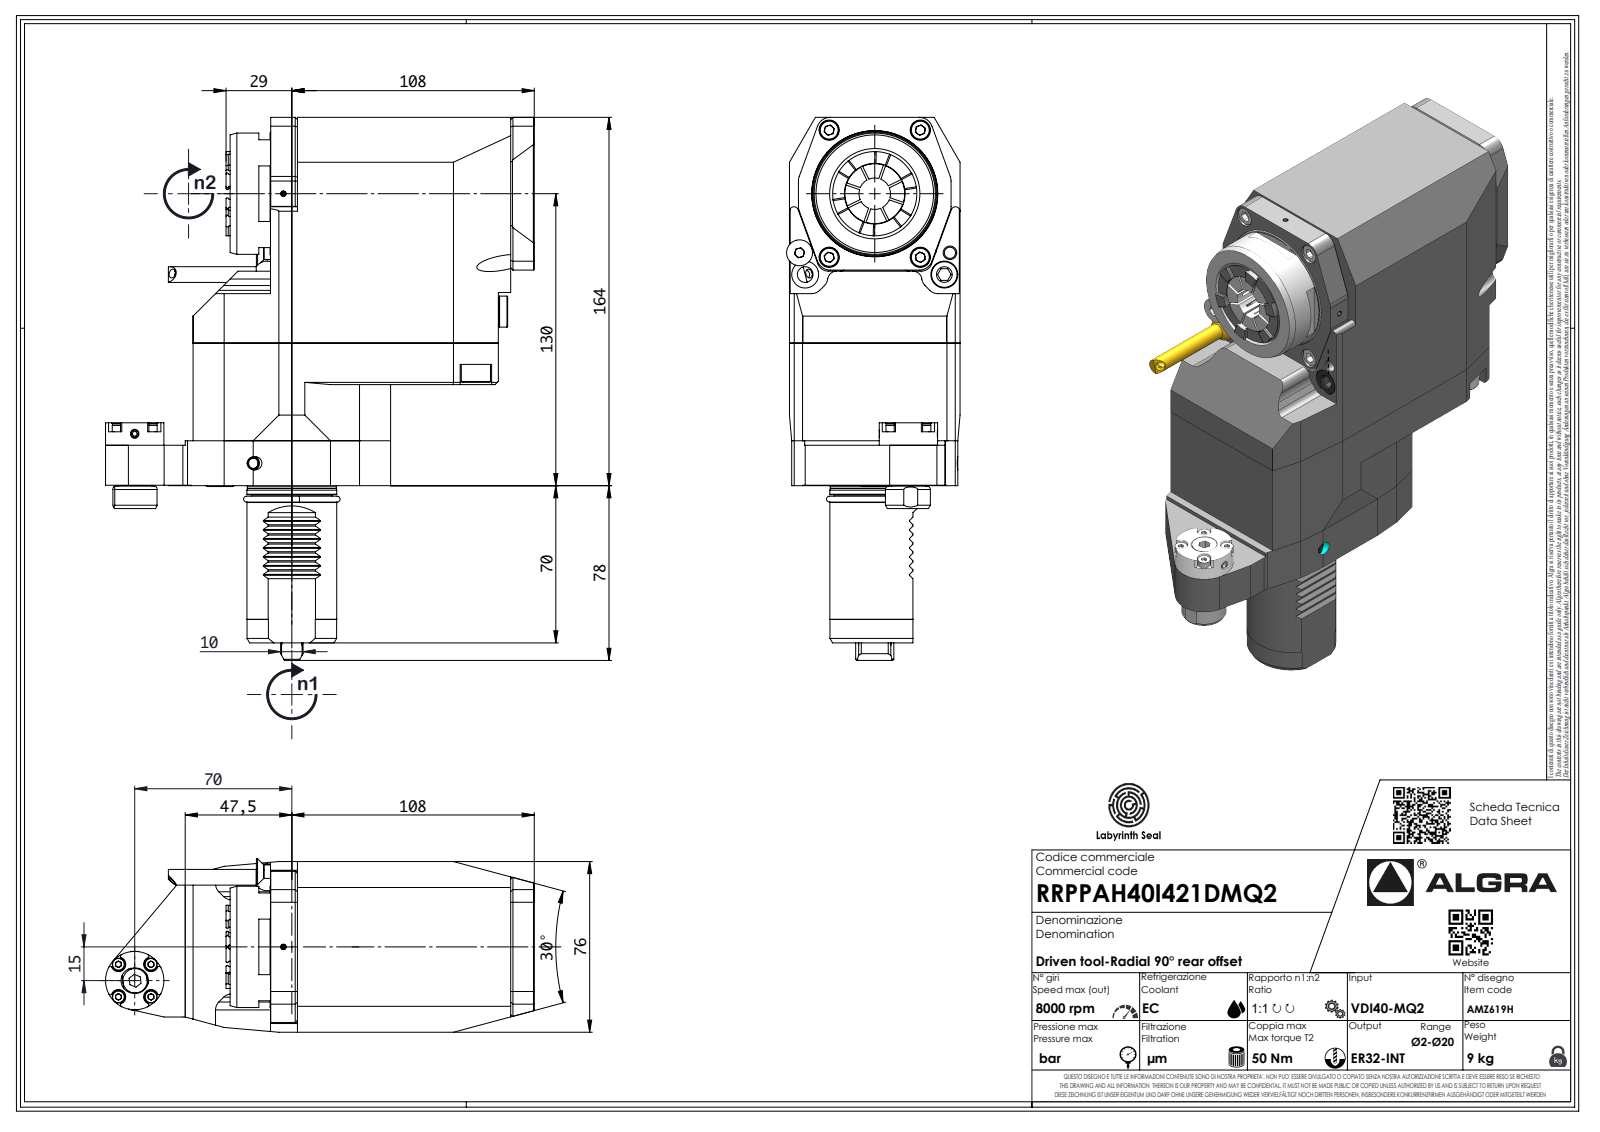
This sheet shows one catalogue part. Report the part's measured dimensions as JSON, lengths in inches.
{"part_name": "RRPPAH40I421DMQ2", "step_written_by": "SolidWorks 2023 (AUTOMOTIVE_DESIGN)", "units": "inches", "bodies": {"solids": 1, "faces": 611, "planar": 415, "cylindrical": 93, "other": 103}, "overall_size": [9.52, 7.539, 2.992], "volume_in3": 91.66, "surface_area_in2": 156.9, "round_holes": [[0.083, 1], [0.157, 1]], "round_bosses_or_shafts": [[2.126, 1], [1.575, 1], [1.571, 1], [1.559, 1], [1.417, 1], [1.024, 1], [0.787, 1], [0.591, 1]], "partial_cylinders_radius": [[0.236, 10], [0.039, 8], [0.118, 8], [0.012, 7], [0.013, 7], [0.02, 7], [0.146, 7], [0.197, 6]], "face_to_face_distances": [2.992, 6.457, 5.354, 0.65, 3.465, 1.772, 4.685, 6.004, 1.89, 2.539]}
